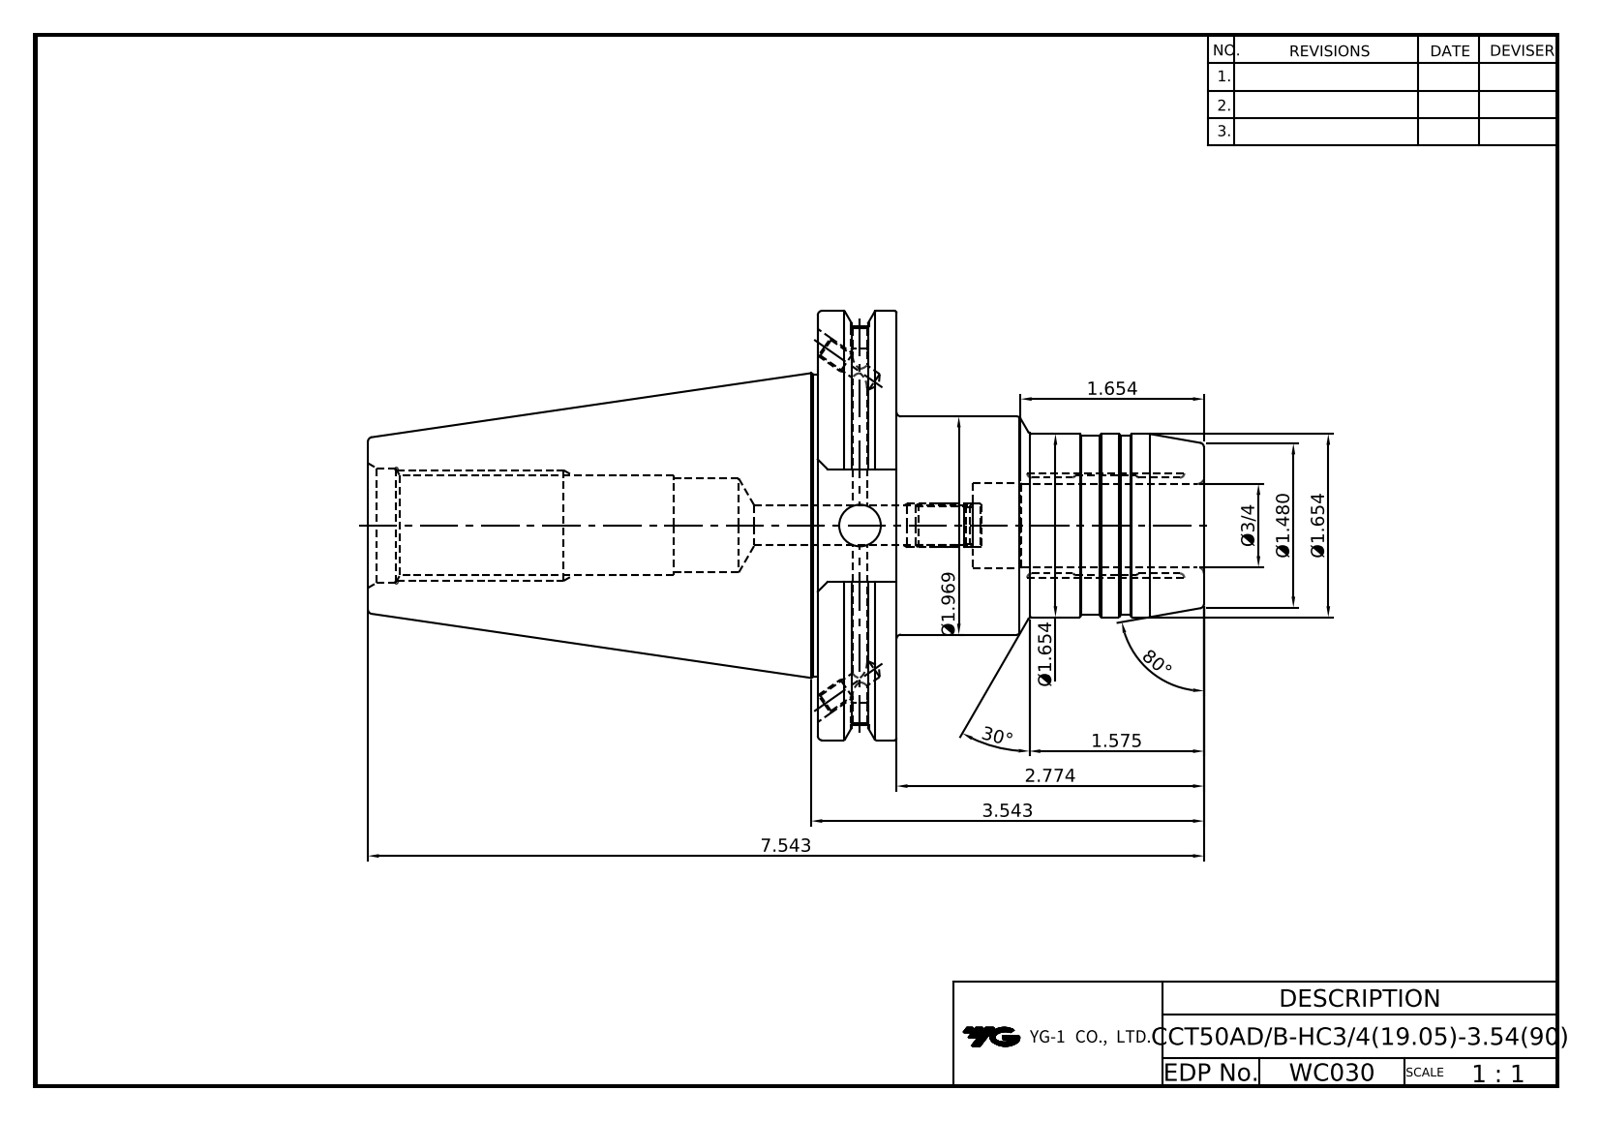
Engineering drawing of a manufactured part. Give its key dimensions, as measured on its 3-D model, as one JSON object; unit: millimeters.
{"part_name": "CCT50ADB-HC19.05-90", "step_written_by": "Autodesk Inventor 2022 (AUTOMOTIVE_DESIGN)", "units": "millimeters", "bodies": {"solids": 1, "faces": 108, "planar": 38, "cylindrical": 32, "other": 38}, "overall_size": [191.6, 98.42, 94.69], "volume_mm3": 431048, "surface_area_mm2": 57418, "round_holes": [[3.24, 2], [4.13, 2], [4.2, 2], [5, 2], [8.92, 1], [9.53, 1], [19.05, 1], [19.4, 1], [21.5, 1], [21.97, 1], [26.2, 1]], "round_bosses_or_shafts": [[98.42, 1], [91.29, 1], [69.25, 1], [50, 1], [42, 1], [41, 1]], "face_to_face_distances": [17.55, 88.5, 70.95, 103.1, 120.65, 191.6, 73.03, 25.9, 138.6, 35.5]}
